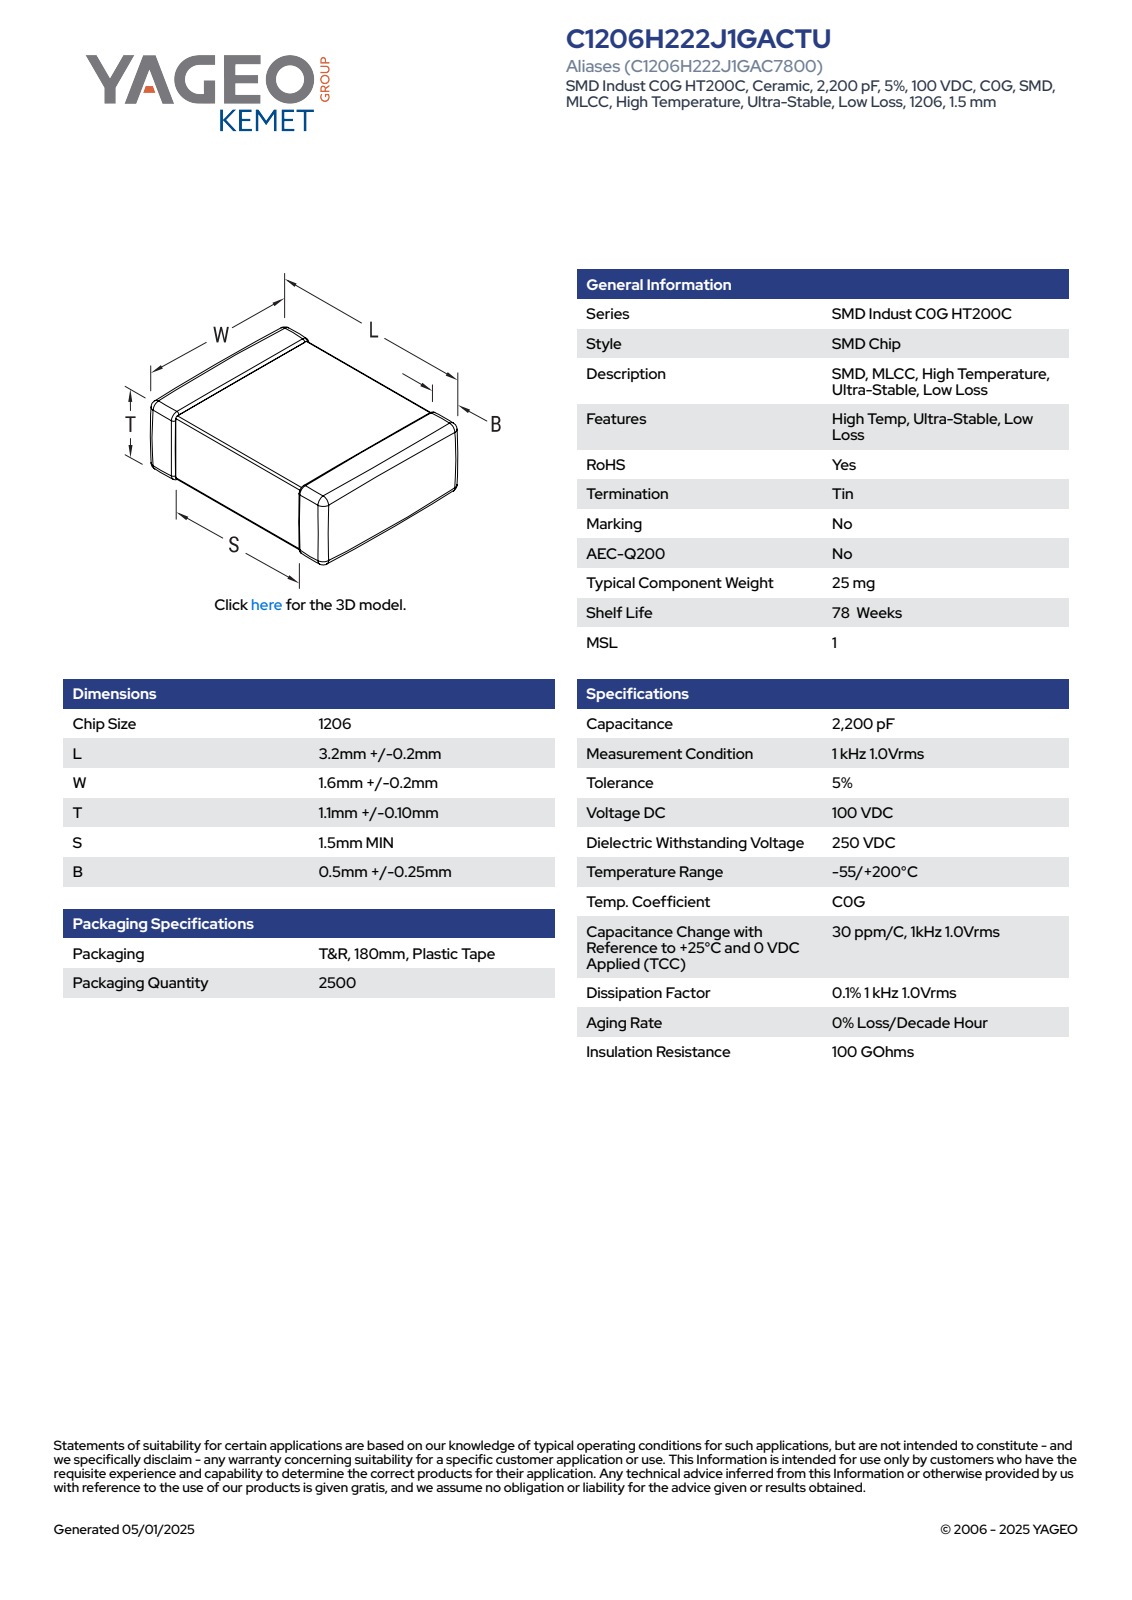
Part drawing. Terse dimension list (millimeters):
name: CCS_CCSTDNOS_1206_L3.4W1.8T1.2B0.75
written by: SolidWorks 2014 (AUTOMOTIVE_DESIGN)
unit: mm
bodies: 4 solids, 125 faces (71 planar, 38 cylindrical, 16 other)
size: 3.4 × 1.8 × 1.2
volume: 7 mm³; area: 24 mm²
face distances: 1.16, 1.12, 1.76, 1.2, 1.72, 3.4, 1.8, 1.17, 1.13, 0.99
